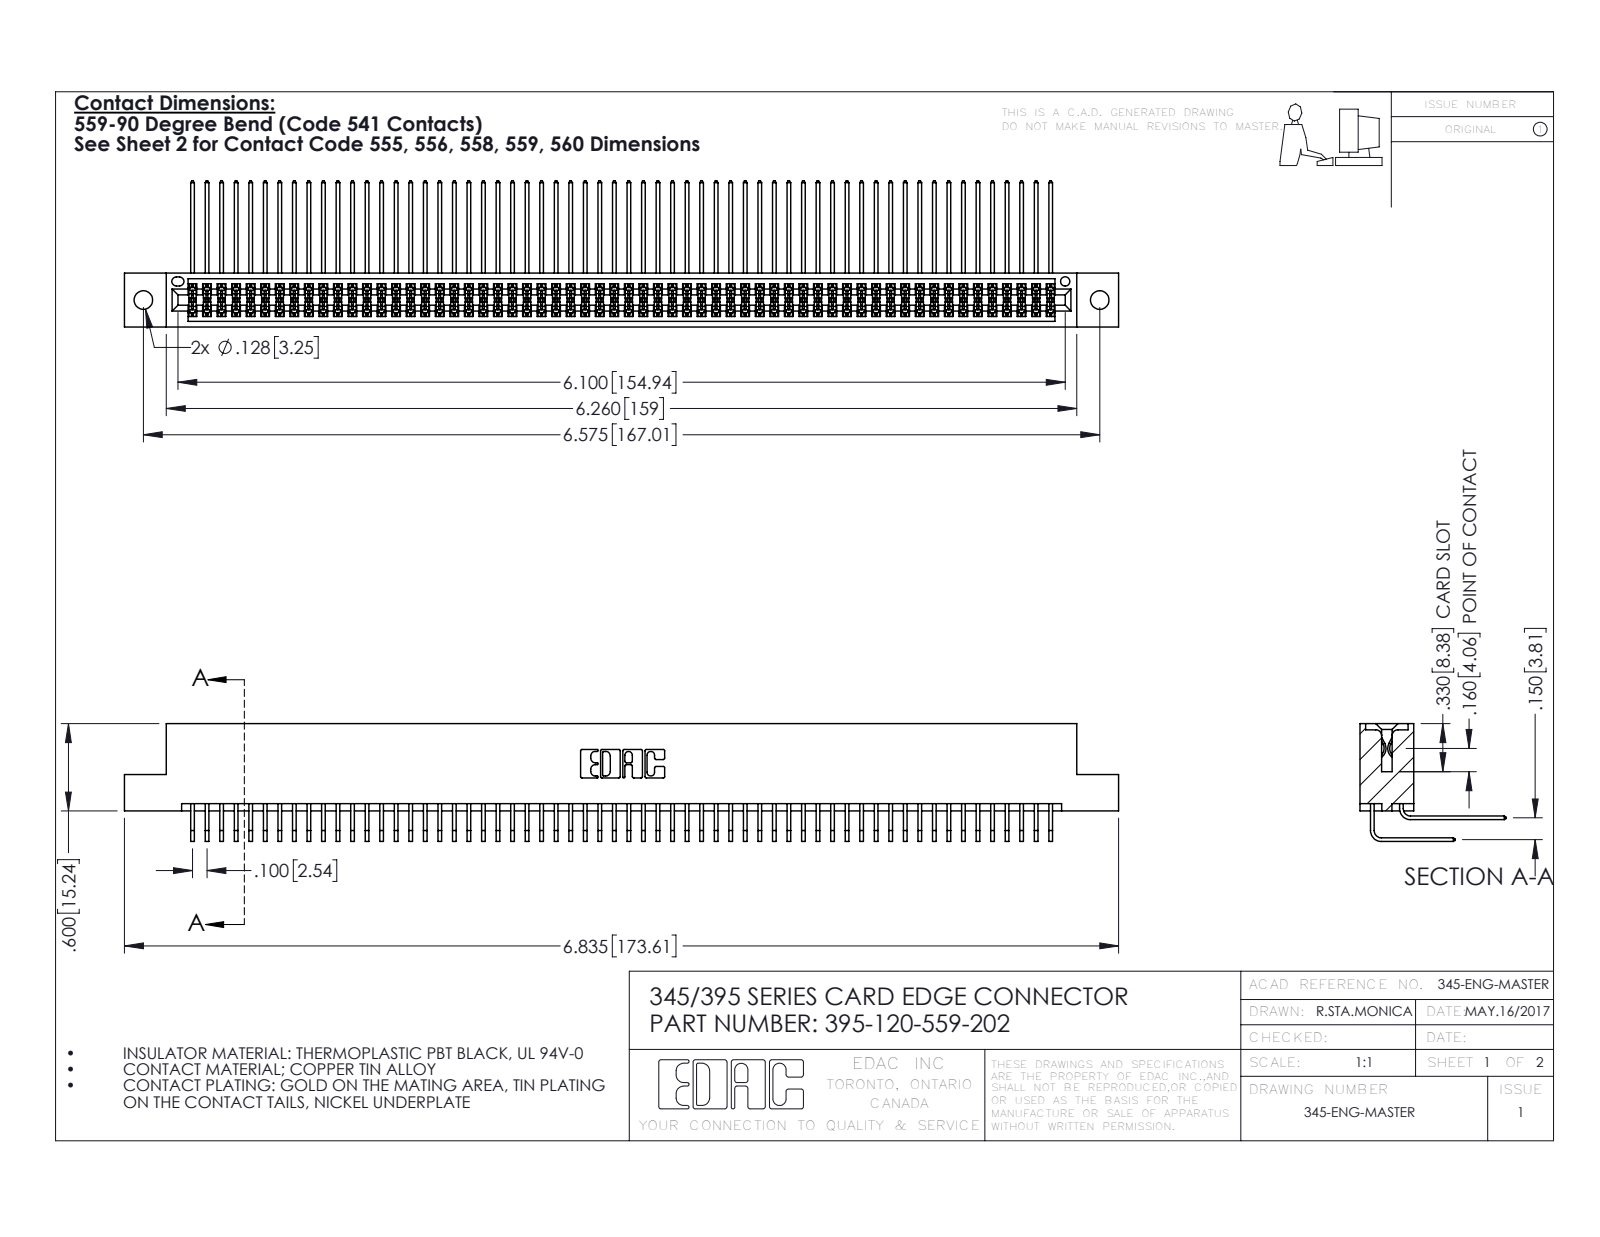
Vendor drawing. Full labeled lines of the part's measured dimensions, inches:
Part name (STEP PRODUCT): 345 Part_Flush Mounting Lugs - 0.128 Dia; 395-120-559-202; 345-292-001_559 Tail - 2; 345-292-001_558 559 Tail - 1
STEP written by: SolidWorks 2016 (CONFIG_CONTROL_DESIGN)
Units: inches
Bodies: 121 solids, 6366 faces (4280 planar, 2086 cylindrical, 0 other)
Overall size (bounding box): 6.835 × 1.005 × 0.809
Volume: 1.079 in³ · Surface area: 45.69 in²
Round holes (diameter × count): ⌀0.128 ×2, ⌀0.064 ×1
Partial cylindrical surfaces — rounded edges, fillets, slot ends (radius × count): R0.006 ×181, R0.01 ×22, R0.007 ×6, R0.031 ×6, R0.026 ×3, R0.014 ×2, R0.019 ×2, R0.022 ×2
Main face-to-face distances: 0.072, 0.298, 0.2, 0.37, 0.098, 0.272, 0.025, 0.225, 0.175, 0.15
Hole centre spacings: 0.27, 6.339, 6.575
